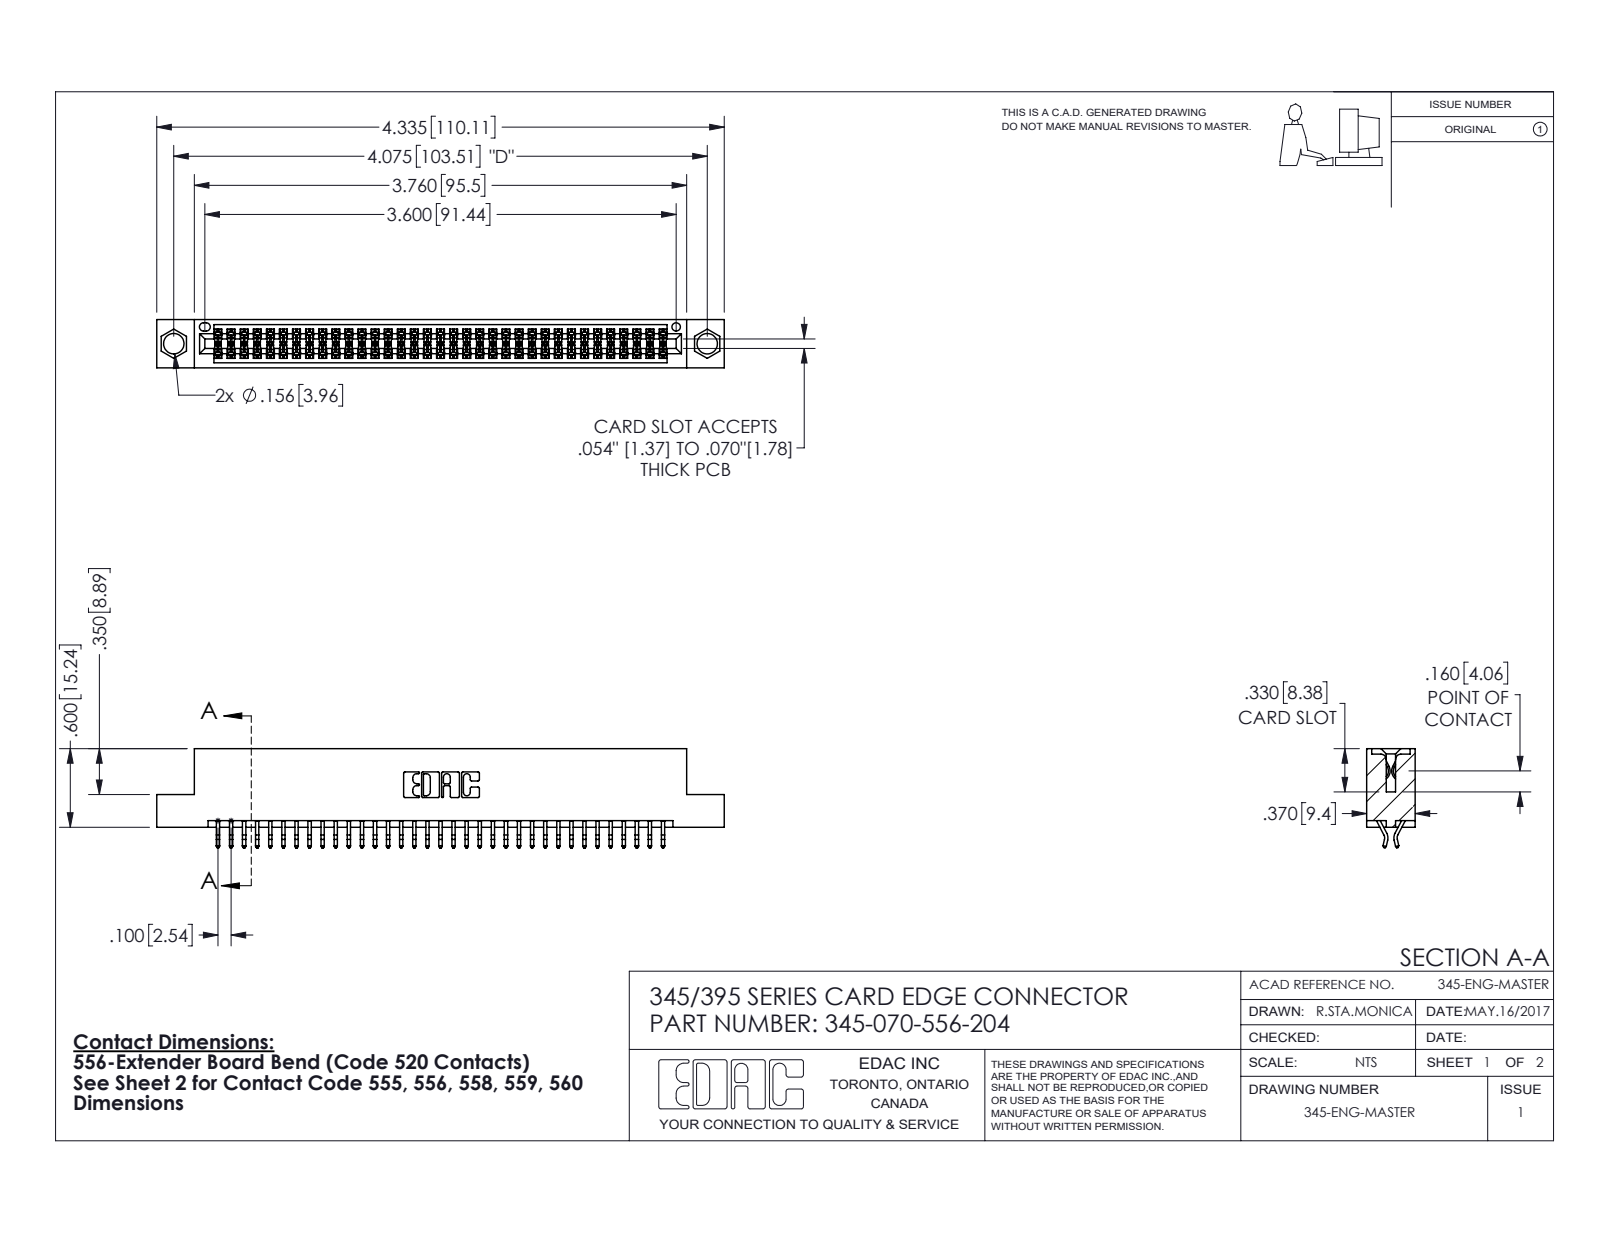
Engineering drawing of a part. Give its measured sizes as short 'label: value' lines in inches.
name: 345 Part_Flush Mounting Lugs - 0.156 Dia-TI; 345-292-001_556 Tail; 345-070-556-204
written by: SolidWorks 2020 (CONFIG_CONTROL_DESIGN)
unit: in
bodies: 71 solids, 4060 faces (2684 planar, 1376 cylindrical, 0 other)
size: 4.335 × 0.757 × 0.37
volume: 0.642 in³; area: 23.57 in²
holes: 2× ⌀0.156, 1× ⌀0.064
rounds: 140× R0.006, 22× R0.01, 6× R0.007, 6× R0.031, 3× R0.026, 2× R0.01, 2× R0.014, 2× R0.019
face distances: 0.298, 0.072, 0.37, 0.2, 0.025, 0.098, 0.272, 0.225, 0.175, 0.149
hole spacings: 0.27, 3.839, 4.075
